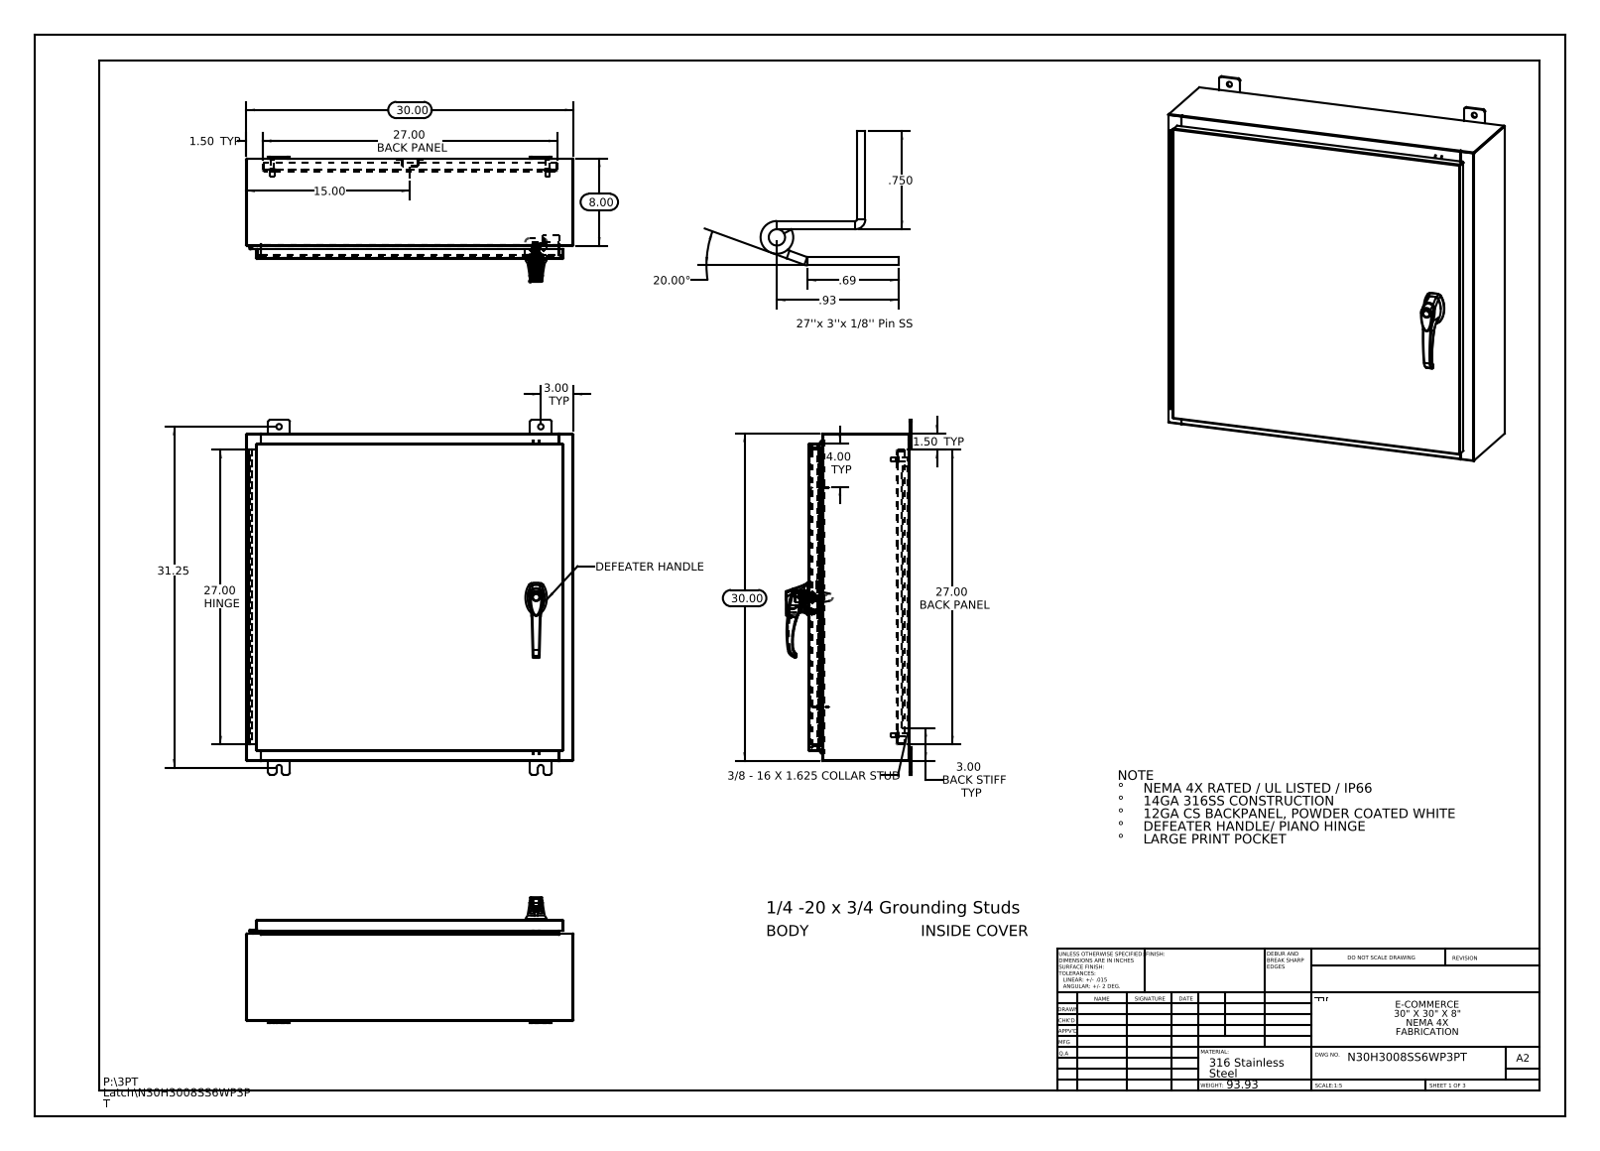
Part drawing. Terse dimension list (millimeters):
name: 00005309_G26103101; N30H3008SS6WP3PT Cover; N30H3008SS6WP3PT Enclosure Stiffener; N30H3008SS6WP3PT Top (+8 more)
written by: SolidWorks 2013 (CONFIG_CONTROL_DESIGN)
unit: mm
bodies: 32 solids, 2614 faces (983 planar, 977 cylindrical, 654 other)
size: 825.5 × 762 × 292
volume: 5 442 000 mm³; area: 5 288 000 mm²
holes: 8× ⌀12.7, 4× ⌀6.4, 3× ⌀3.5, 3× ⌀4.1, 2× ⌀2, 2× ⌀5.2, 2× ⌀8, 2× ⌀11.1, 1× ⌀3.2, 1× ⌀3.2, 1× ⌀5, 1× ⌀7
bosses: 4× ⌀15.9, 4× ⌀9.5, 4× ⌀8.4, 1× ⌀30, 1× ⌀19, 1× ⌀17.3, 1× ⌀16.8, 1× ⌀16.2
rounds: 37× R3, 33× R0.2, 28× R0.3, 24× R4.8, 22× R2.2, 15× R1, 12× R0.7, 6× R0.2
face distances: 1.9, 231.8, 760.1, 229.9, 2.6, 233.7, 25.4, 206.4, 27.3, 204.5
hole spacings: 212.6, 7.5, 15.9, 21.4, 31.8, 33.4, 39.6, 47.2
